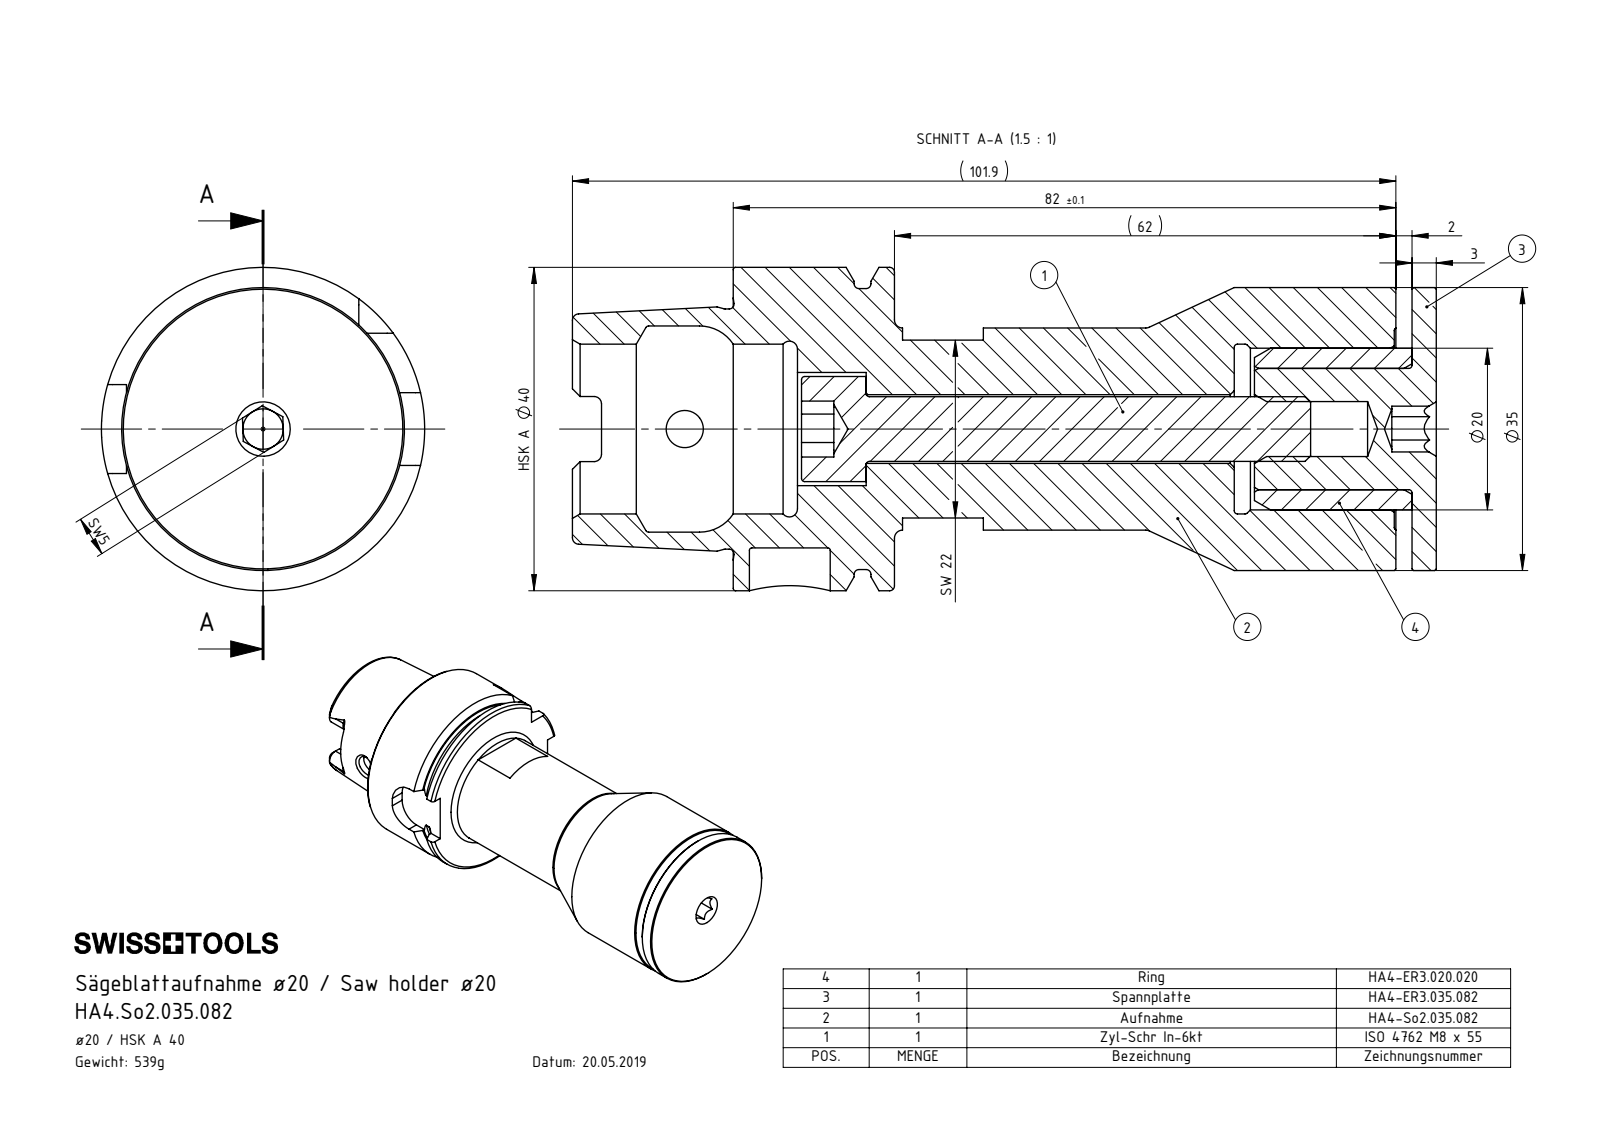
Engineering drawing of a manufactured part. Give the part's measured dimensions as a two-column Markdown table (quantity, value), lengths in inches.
| quantity | value |
| --- | --- |
| part name | ISO 4762 - M8 x 55_PreviewCfg; HA4.So2.035.082; HA4-ER3.020.020_A; HA4-ER3.035.082_A (+1 more) |
| STEP written by | SolidWorks 2017 (AUTOMOTIVE_DESIGN) |
| units | inches |
| bodies | 4 solids, 190 faces (83 planar, 41 cylindrical, 66 other) |
| overall size | 4.209 × 1.575 × 1.575 |
| volume | 4.189 in³ |
| surface area | 40.39 in² |
| round holes (diameter × count) | 0.181 × 1, 0.268 × 1, 0.335 × 1, 0.394 × 1, 0.551 × 1, 0.591 × 1, 0.787 × 1, 0.827 × 1, 1.004 × 1 |
| round bosses / shafts (diameter × count) | 1.575 × 1, 1.378 × 1, 1.368 × 1, 1.17 × 1, 0.984 × 1, 0.512 × 1, 0.315 × 1 |
| partial cylindrical surfaces (radius × count) | 0.035 × 6, 0.074 × 4, 0.177 × 4 |
| main face-to-face distances | 0.118, 2.522, 2.64, 0.197, 2.443, 0.079, 0.785, 3.228, 3.307, 3.425 |
